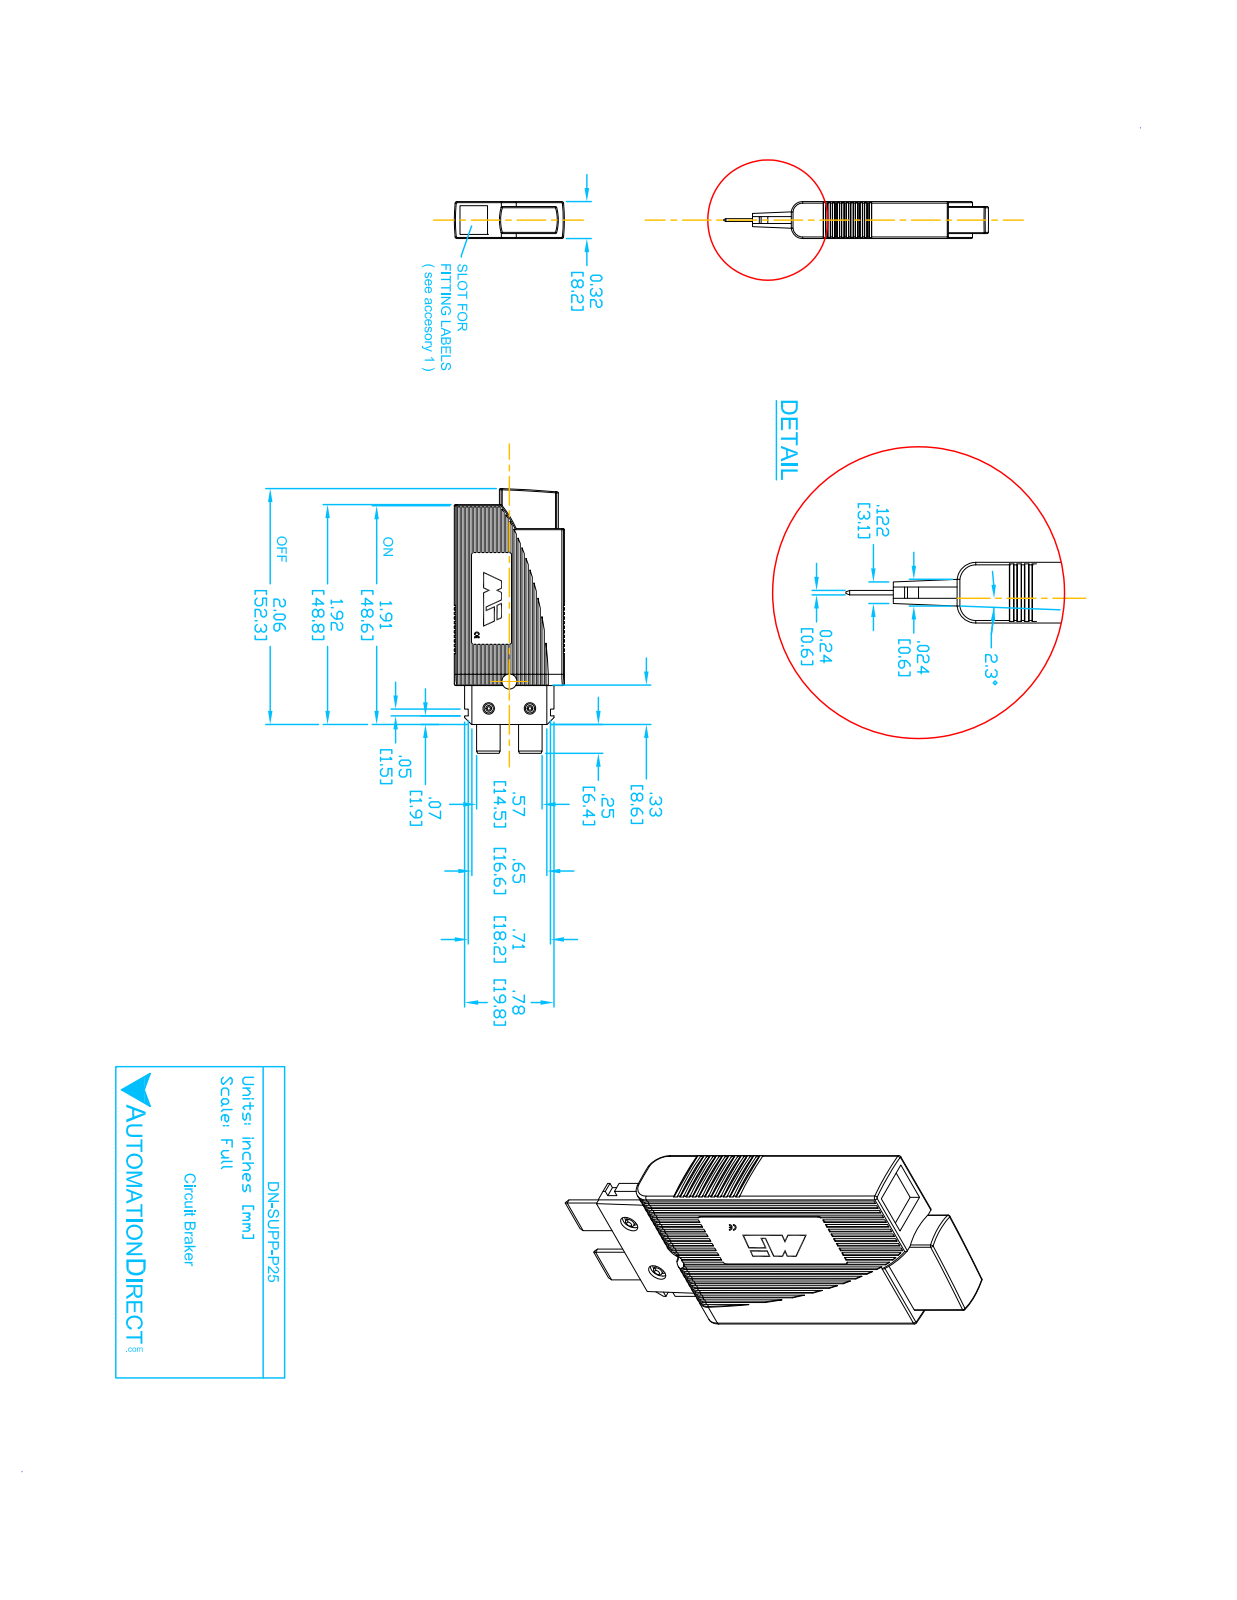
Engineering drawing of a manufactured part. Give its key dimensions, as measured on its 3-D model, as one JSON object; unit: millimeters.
{"part_name": "DN-SUPP-P25", "step_written_by": "SolidWorks 2017 (AUTOMOTIVE_DESIGN)", "units": "millimeters", "bodies": {"solids": 1, "faces": 95, "planar": 47, "cylindrical": 28, "other": 20}, "overall_size": [55.4, 24.4, 8.2], "volume_mm3": 8280, "surface_area_mm2": 3375, "partial_cylinders_radius": [[0.3, 21], [4, 2], [55, 1], [59.2, 1], [60, 1]], "face_to_face_distances": [8.2, 24.4, 3.8, 4.4, 0.8, 7.4, 3, 3.6, 0.6, 3.6]}
